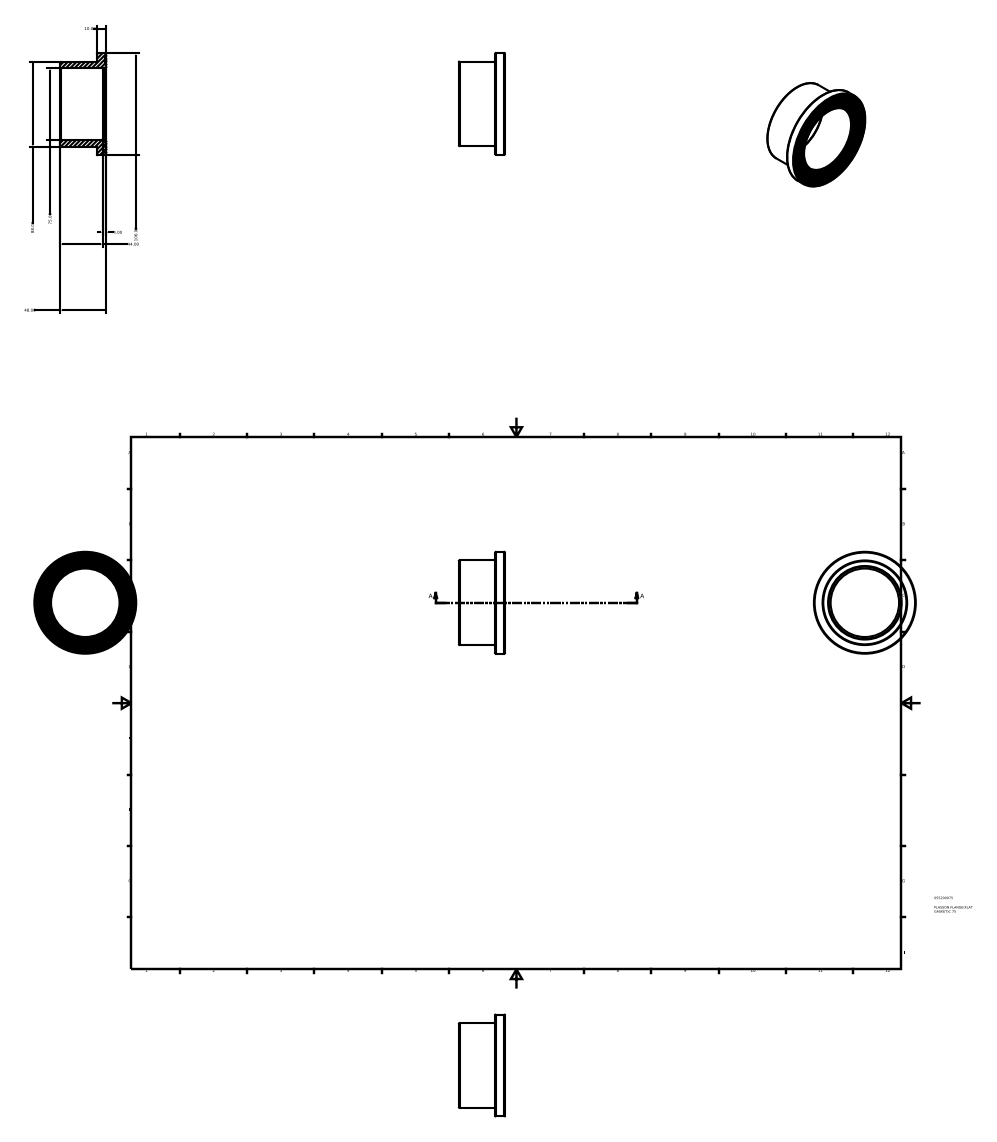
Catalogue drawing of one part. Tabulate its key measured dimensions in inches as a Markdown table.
| quantity | value |
| --- | --- |
| part name | 055200075 |
| STEP written by | Autodesk Inventor 2015 (AUTOMOTIVE_DESIGN) |
| units | inches |
| bodies | 1 solid, 28 faces (9 planar, 4 cylindrical, 15 other) |
| overall size | 4.173 × 4.173 × 1.89 |
| volume | 6.429 in³ |
| surface area | 54.53 in² |
| round holes (diameter × count) | 2.805 × 1, 2.953 × 1 |
| round bosses / shafts (diameter × count) | 4.173 × 1, 3.465 × 1 |
| main face-to-face distances | 1.496, 1.89, 0.394, 1.831, 0.335, 0.059, 1.732, 0.236, 0.098, 0.157 |
